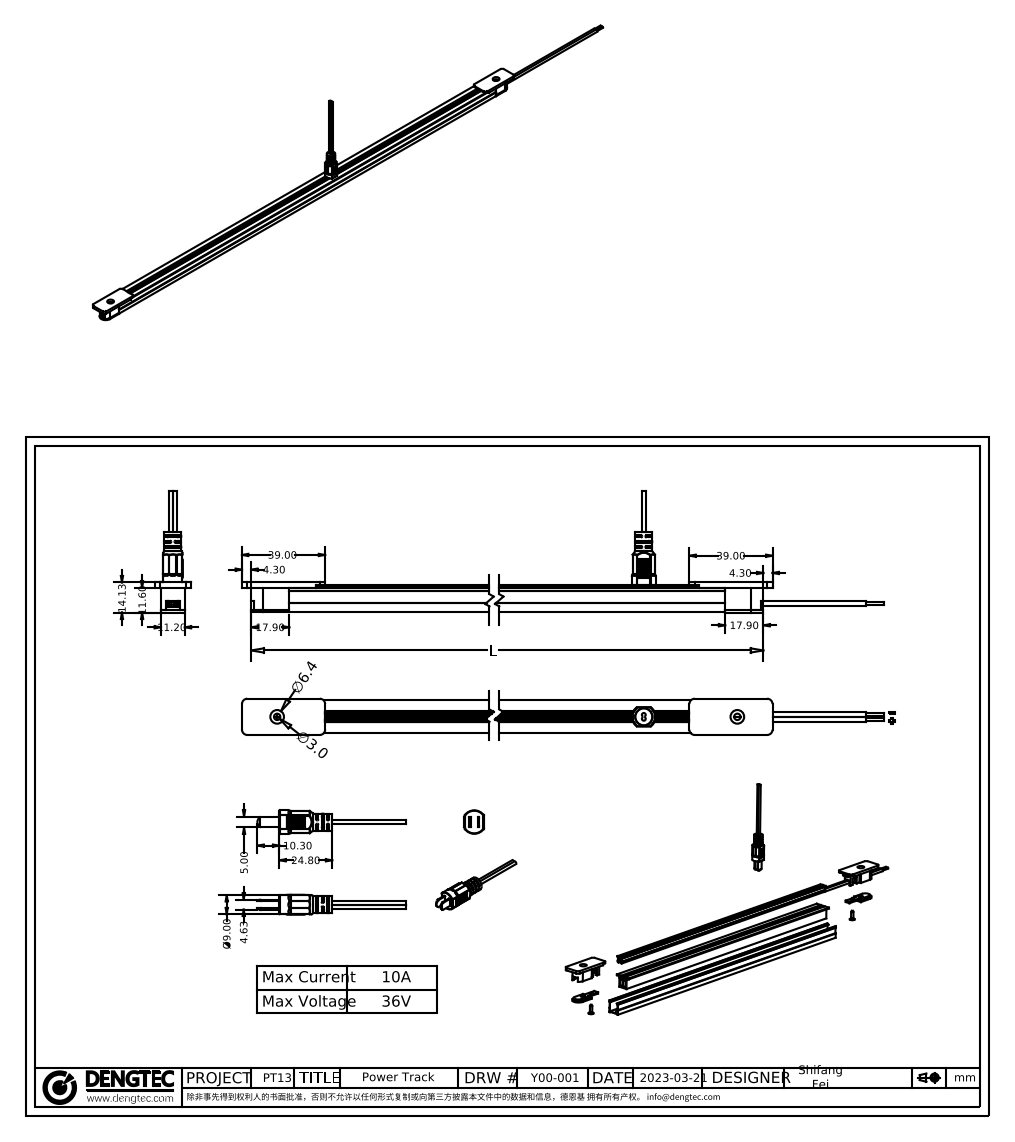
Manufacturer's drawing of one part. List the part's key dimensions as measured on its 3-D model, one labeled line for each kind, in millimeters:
Part name (STEP PRODUCT): 电线; 堵头2; 铜槽; 导电槽15.4X8.5 (+3 more)
STEP written by: SolidWorks 2018 (CONFIG_CONTROL_DESIGN)
Units: millimetres
Bodies: 9 solids, 504 faces (268 planar, 176 cylindrical, 60 other)
Overall size (bounding box): 378 × 63.35 × 15.5
Volume: 21 910 mm³ · Surface area: 55 815 mm²
Round holes (diameter × count): ⌀2.5 ×2
Round bosses / shafts (diameter × count): ⌀2.4 ×2, ⌀1.8 ×2, ⌀1.3 ×2, ⌀8 ×1, ⌀7.1 ×1, ⌀5 ×1
Partial cylindrical surfaces — rounded edges, fillets, slot ends (radius × count): R0.15 ×44, R0.2 ×18, R0.5 ×14, R2 ×6, R0.4 ×4, R0.7 ×4, R0.8 ×2, R1 ×2
Main face-to-face distances: 0.9, 4.1, 3.2, 11.3, 3.1, 7.2, 1, 7.6, 2.15, 1.95
Hole centre spacings: 3.5
